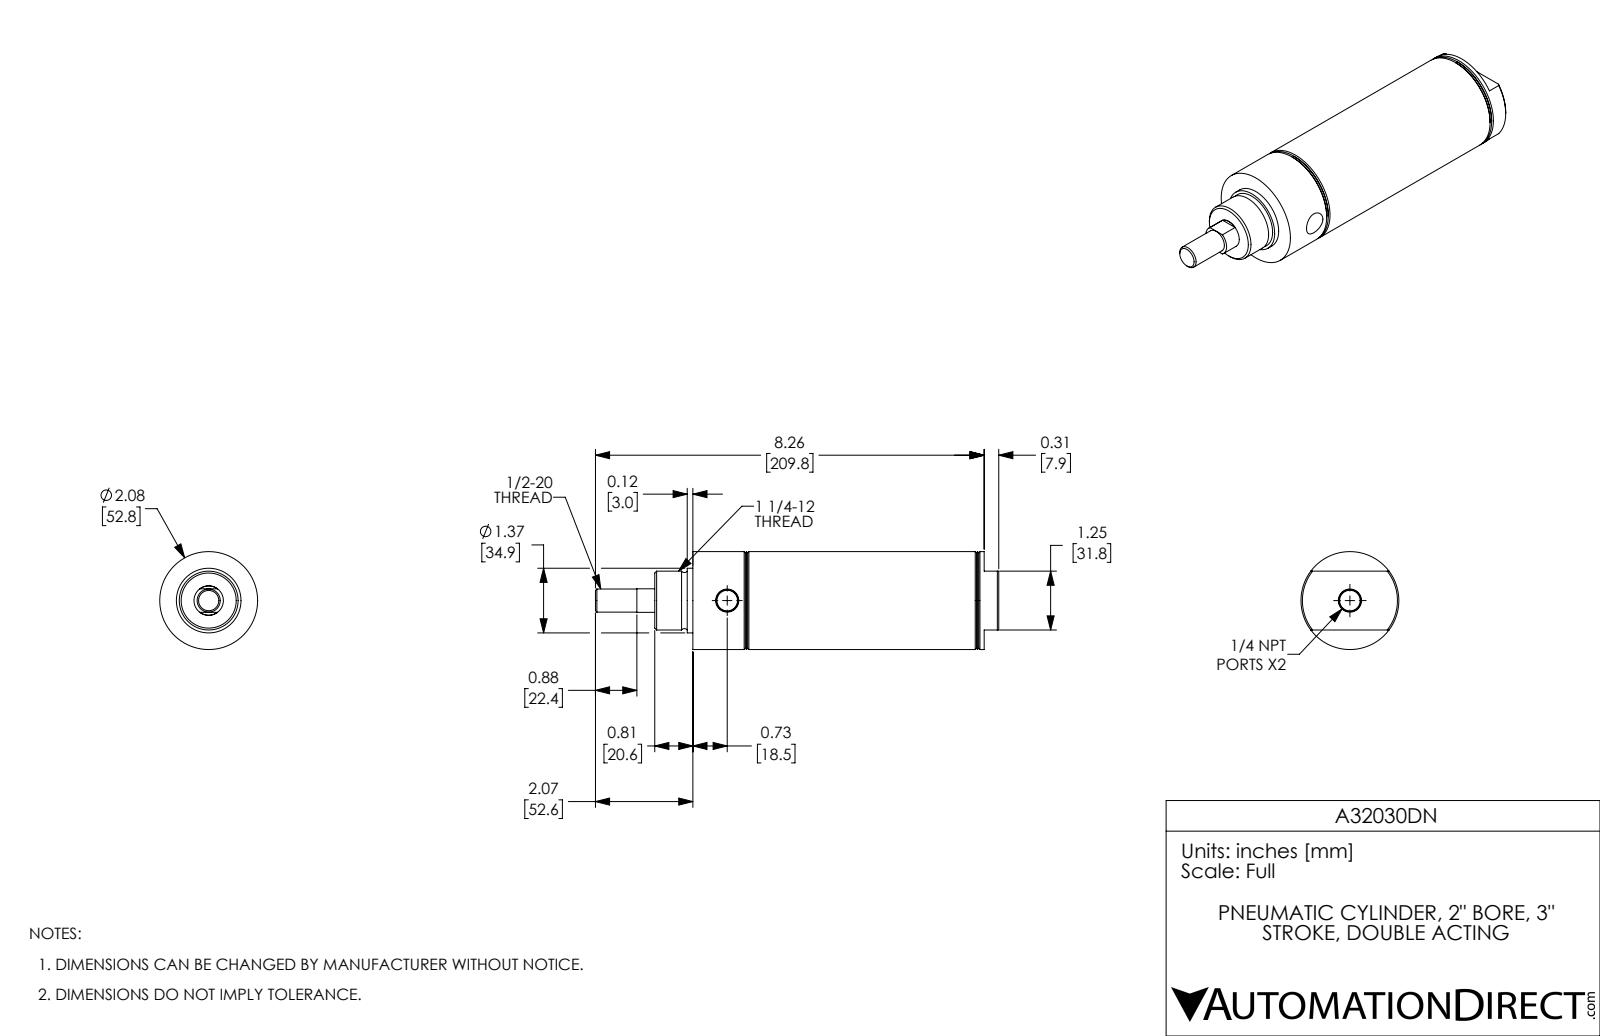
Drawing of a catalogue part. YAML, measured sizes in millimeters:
part_name: "A32030DN-Rod; A32030DN-MainBody; A32030DN"
step_written_by: "SolidWorks 2017 (AUTOMOTIVE_DESIGN)"
units: millimeters
bodies: {solids: 2, faces: 77, planar: 20, cylindrical: 24, other: 33}
overall_size: [217.7, 52.8, 52.8]
volume: 234300
surface_area: 70060
round_holes:
  - {diameter: 11.1, count: 2}
  - {diameter: 15.9, count: 1}
  - {diameter: 50.8, count: 1}
round_bosses_or_shafts:
  - {diameter: 52.8, count: 1}
  - {diameter: 34.9, count: 1}
  - {diameter: 31.8, count: 1}
  - {diameter: 12.5, count: 1}
face_to_face_distances: [38.1, 127, 12.7, 88.9, 76.2, 50.8, 165.1, 114.3, 7.9, 30.2]
